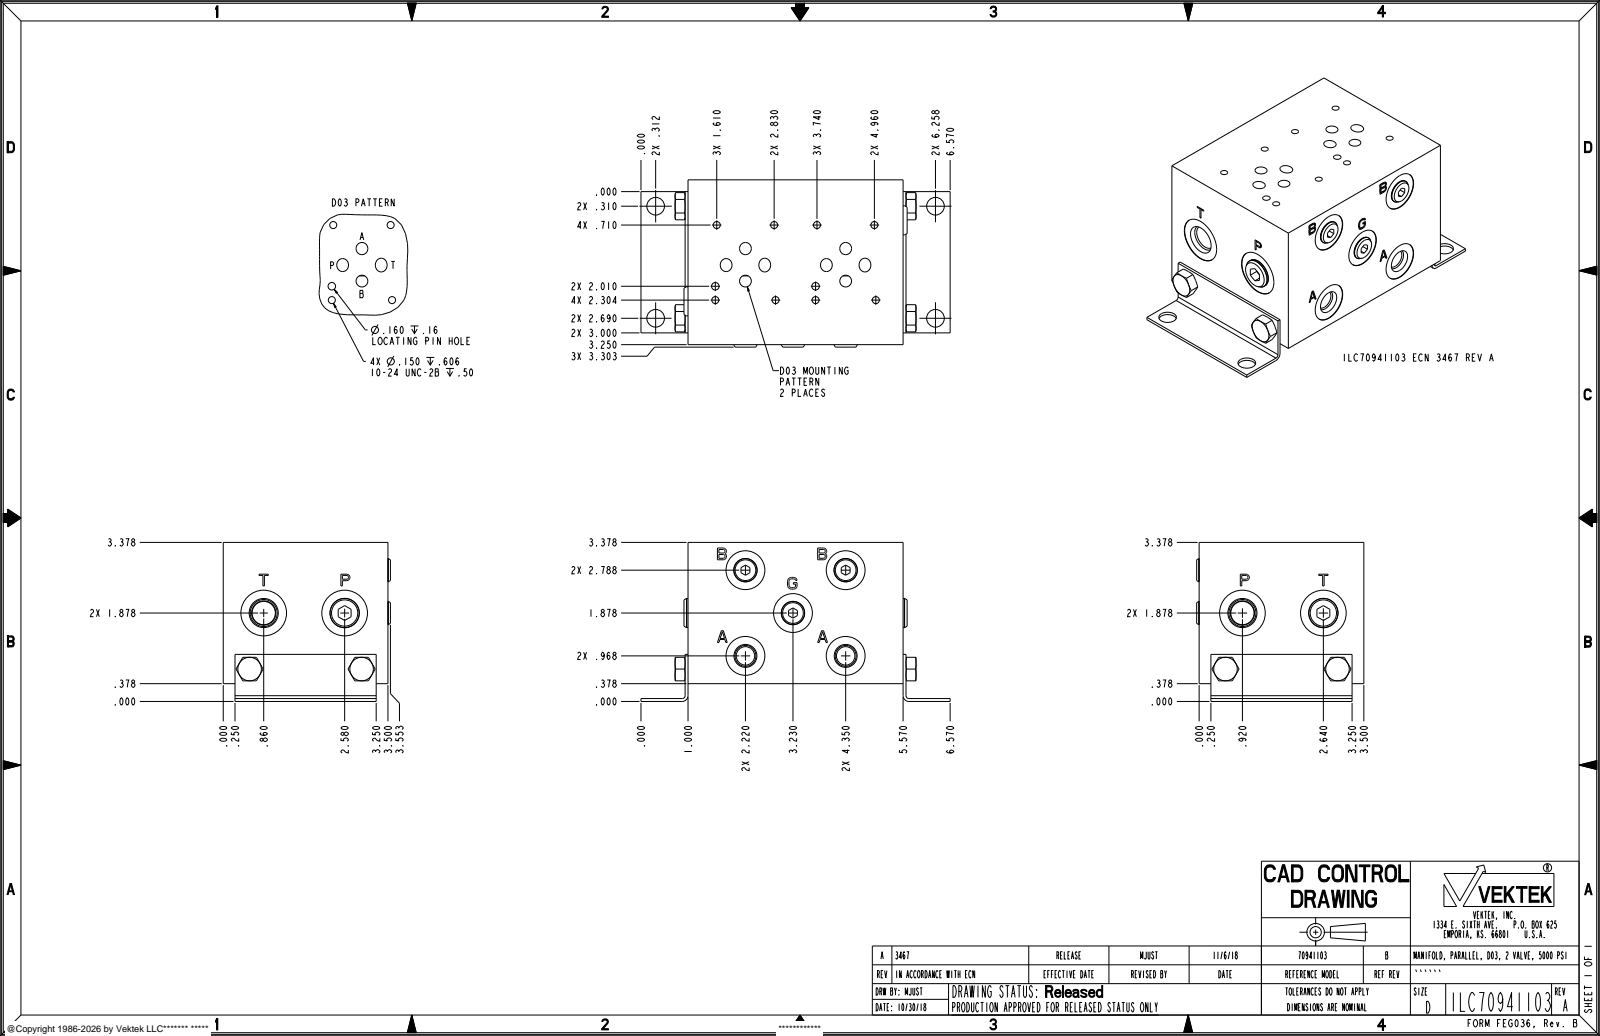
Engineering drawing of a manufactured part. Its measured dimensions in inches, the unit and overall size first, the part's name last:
Units: inches
Overall size (bounding box): 6.57 × 3.553 × 3.378
Round holes (diameter × count): ⌀0.15 ×8, ⌀0.25 ×8, ⌀0.392 ×5, ⌀0.825 ×5, ⌀0.375 ×4, ⌀0.16 ×2, ⌀0.515 ×2, ⌀0.97 ×2
Round bosses / shafts (diameter × count): ⌀0.48 ×2
Partial cylindrical surfaces — rounded edges, fillets, slot ends (radius × count): R0.06 ×2, R0.125 ×2
Main face-to-face distances: 3, 3.5, 0.062, 4.57, 0.316, 3.316, 0.378, 3.378, 4.632, 4.694
Hole centre spacings: 2.13, 1.337, 1.594, 2.026, 0.757, 2.13, 0.294, 0.65
Volume: 45.73 in³ · Surface area: 132.2 in²
Bodies: 1 solid, 565 faces (333 planar, 84 cylindrical, 148 other)
Part name (STEP PRODUCT): ILC70941103
STEP written by: PRO/ENGINEER BY PARAMETRIC TECHNOLOGY CORPORATION, 2013320 (AUTOMOTIVE_DESIGN)
